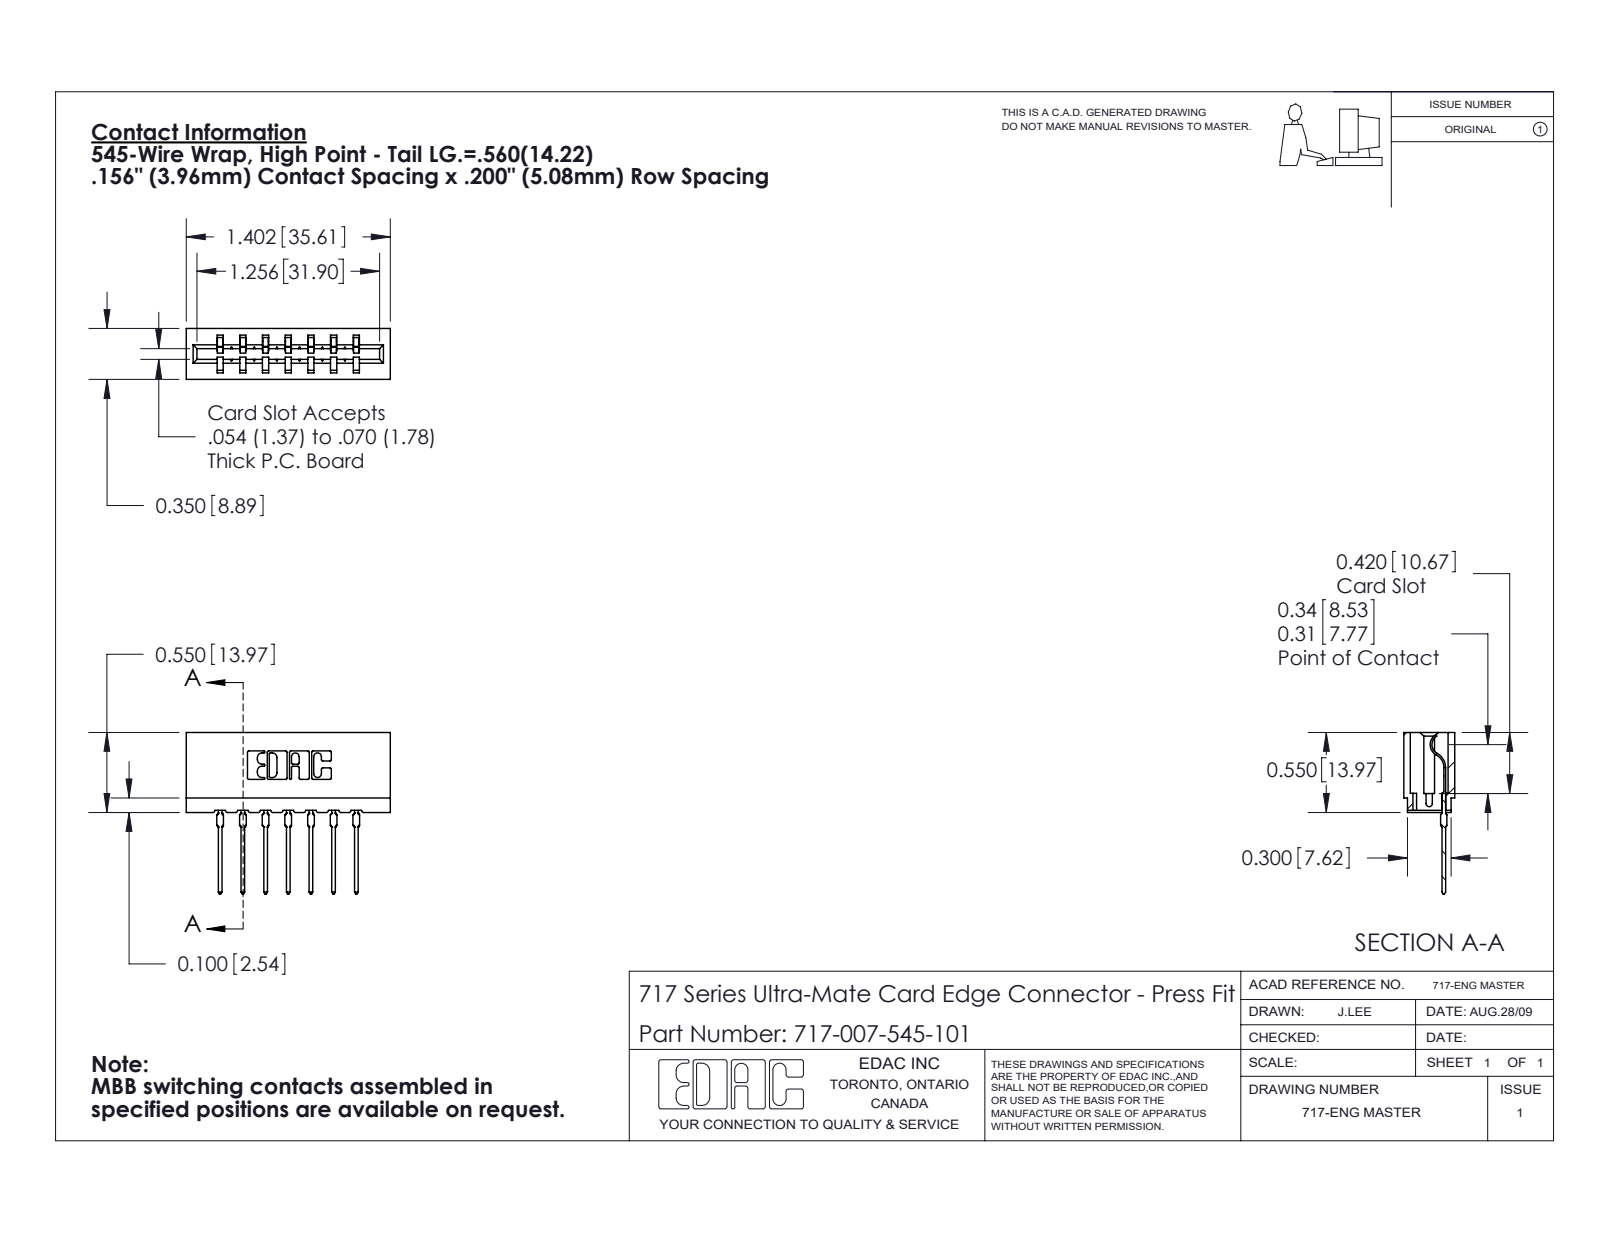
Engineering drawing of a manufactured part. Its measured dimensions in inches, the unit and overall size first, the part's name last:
Units: inches
Overall size (bounding box): 1.402 × 1.109 × 0.35
Partial cylindrical surfaces — rounded edges, fillets, slot ends (radius × count): R0.01 ×22, R0.015 ×14, R0.021 ×14, R0.007 ×6, R0.031 ×6, R0.005 ×4, R0.011 ×4, R0.026 ×3
Main face-to-face distances: 0.212, 0.156, 0.138, 0.35, 0.198, 0.312, 0.468, 0.624, 0.042, 0.27
Volume: 0.194 in³ · Surface area: 6.516 in²
Bodies: 8 solids, 885 faces (530 planar, 173 cylindrical, 182 other)
Part name (STEP PRODUCT): 717-007-545-101; 745-292-001_545; 717 Part_Insulator Option - 06
STEP written by: SolidWorks 2020 (CONFIG_CONTROL_DESIGN)
